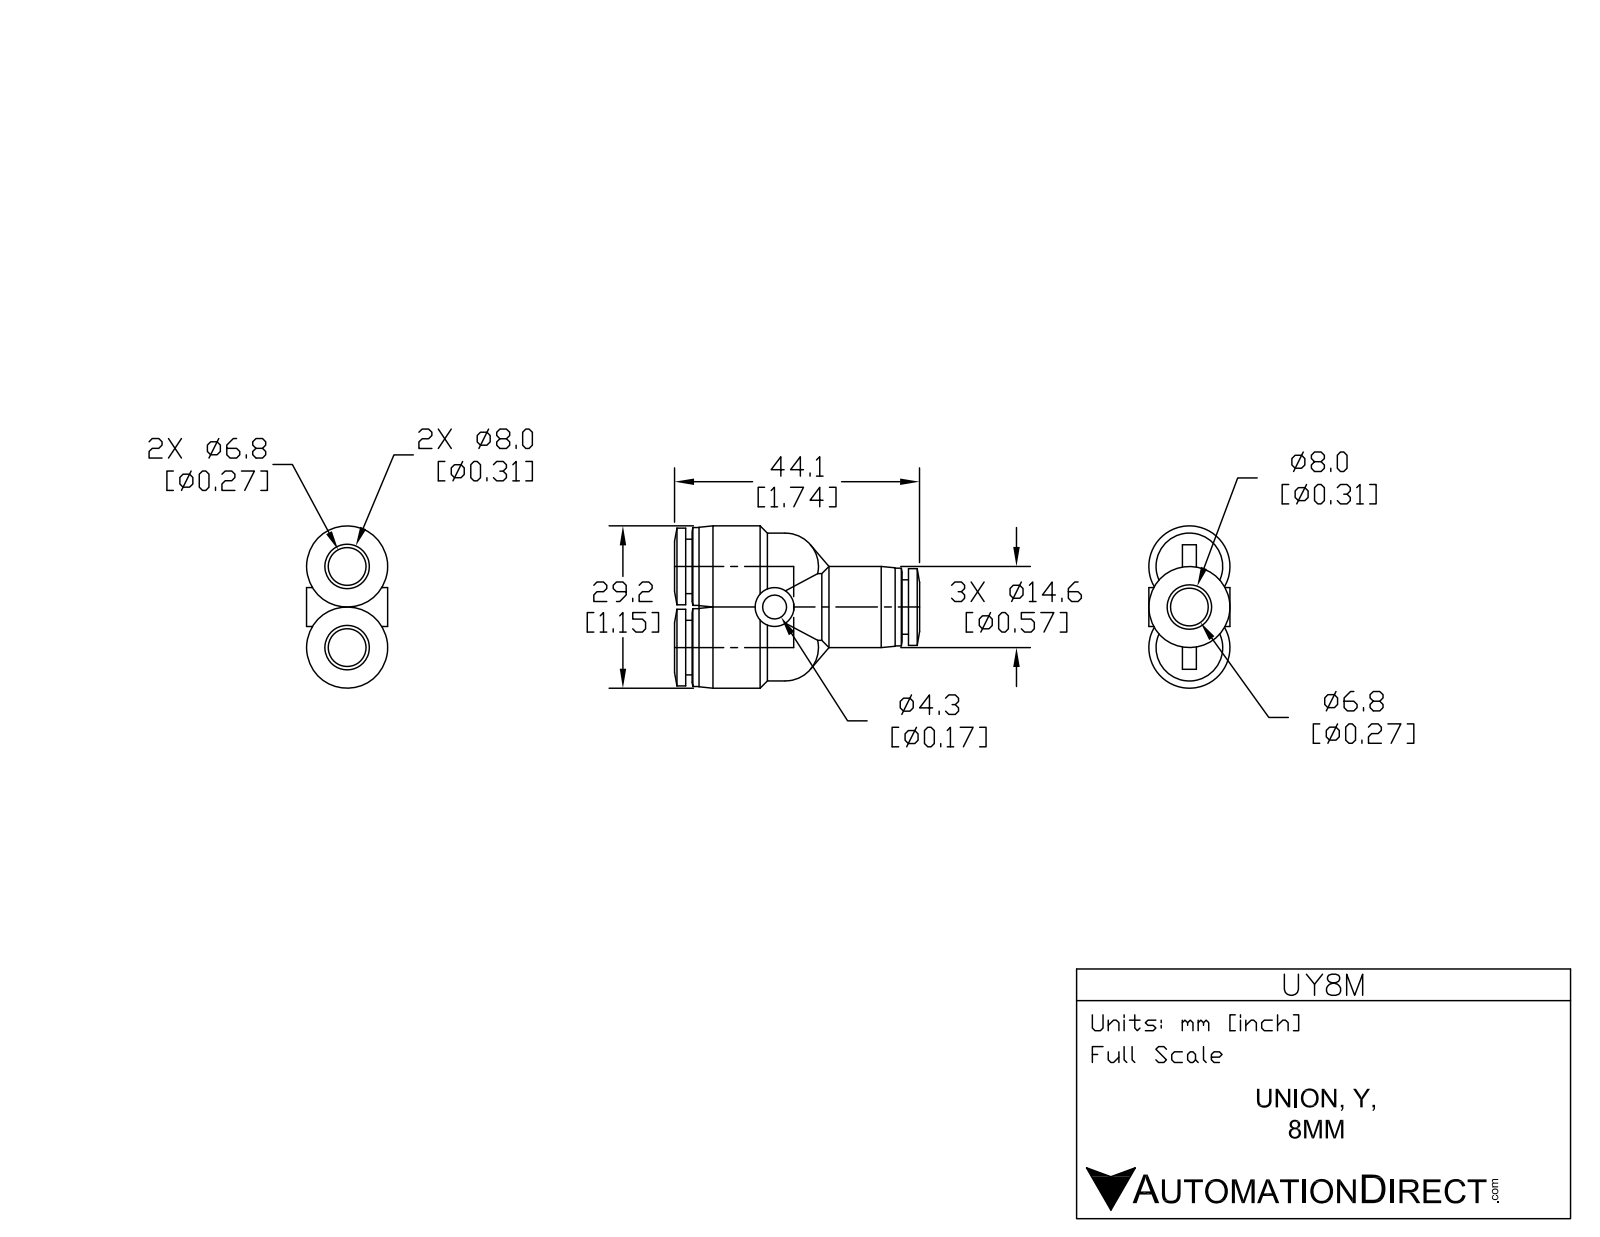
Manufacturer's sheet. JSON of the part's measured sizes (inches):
{"part_name": "UY8M", "step_written_by": "SolidWorks 2015 (AUTOMOTIVE_DESIGN)", "units": "inches", "bodies": {"solids": 1, "faces": 105, "planar": 25, "cylindrical": 40, "other": 40}, "overall_size": [1.701, 1.15, 0.575], "volume_in3": 0.412, "surface_area_in2": 8.734, "round_holes": [[0.327, 3], [0.169, 1]], "round_bosses_or_shafts": [[0.575, 3], [0.551, 3], [0.543, 3], [0.386, 3], [0.472, 1], [0.276, 1]], "partial_cylinders_radius": [[0.236, 2]], "face_to_face_distances": [0.045, 1.498, 0.654, 0.89, 0.608, 0.844, 1.543, 1.453, 0.236, 0.575], "hole_center_spacings": [0.287, 0.575]}
